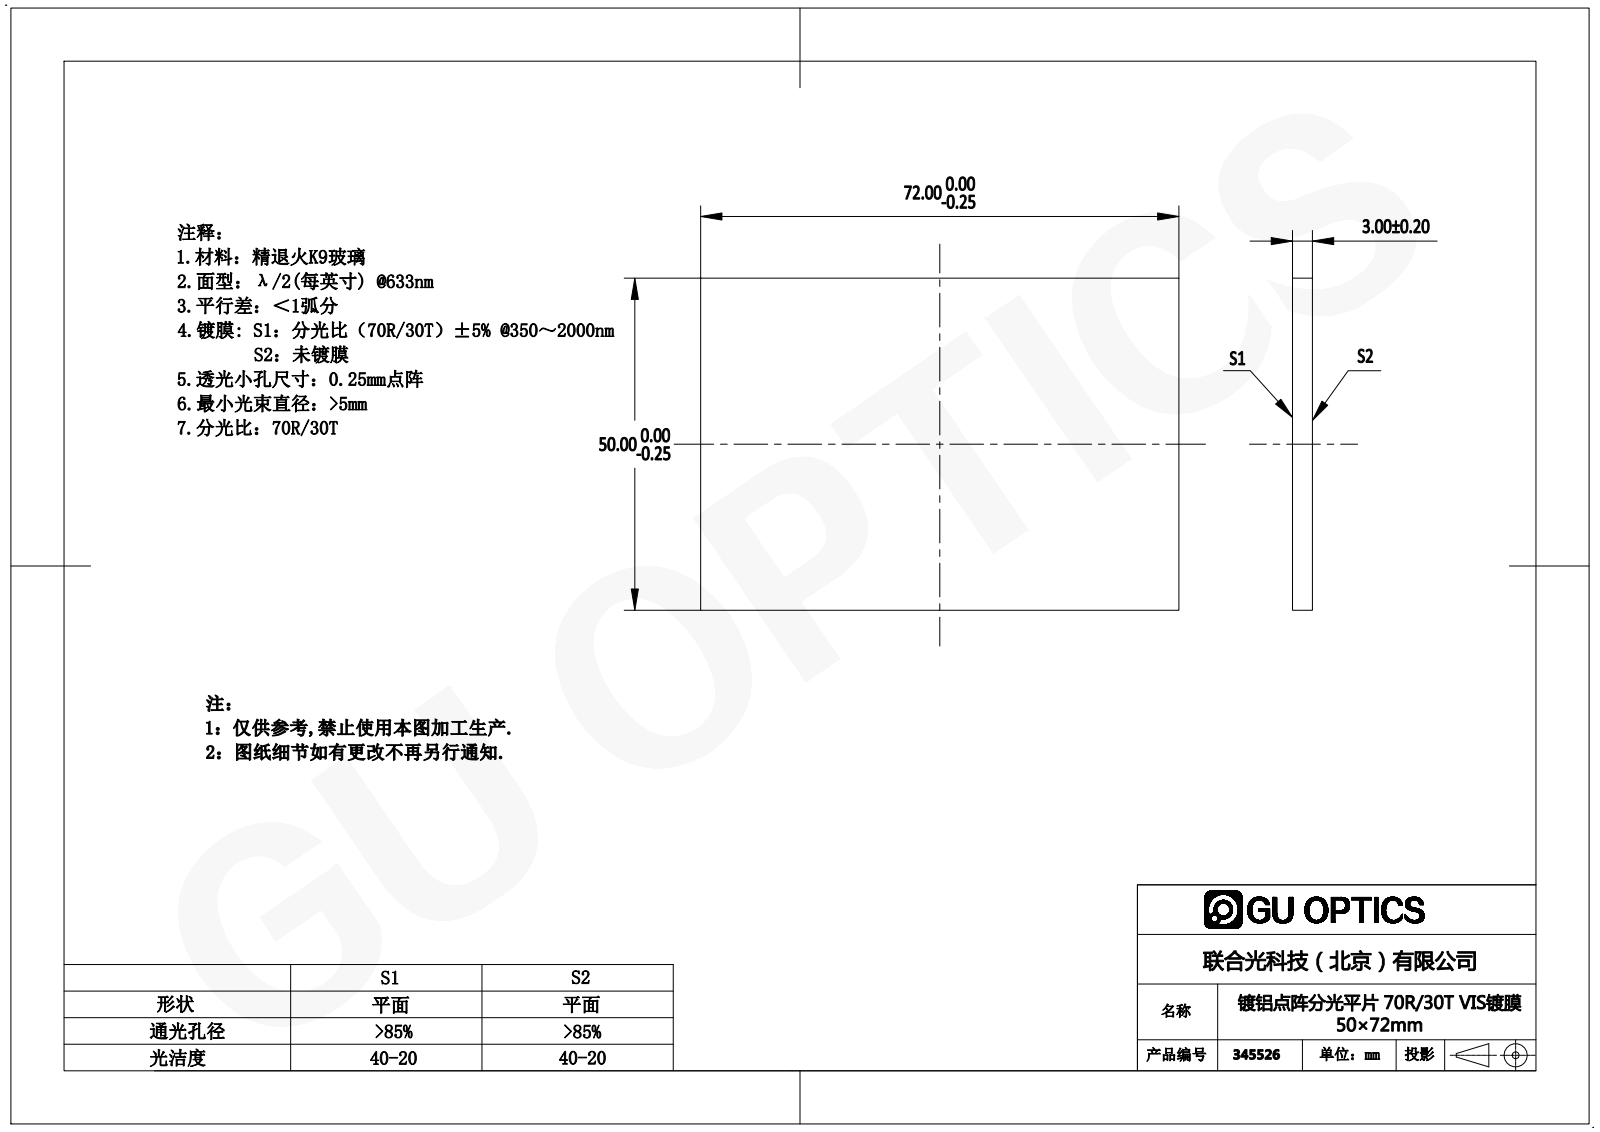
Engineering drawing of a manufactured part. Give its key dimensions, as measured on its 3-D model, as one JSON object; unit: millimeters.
{"part_name": "345508", "step_written_by": "SolidWorks 2016 (AUTOMOTIVE_DESIGN)", "units": "millimeters", "bodies": {"solids": 1, "faces": 6, "planar": 6, "cylindrical": 0, "other": 0}, "overall_size": [72, 50, 3], "volume_mm3": 10800, "surface_area_mm2": 7932, "face_to_face_distances": [3, 50, 72]}
